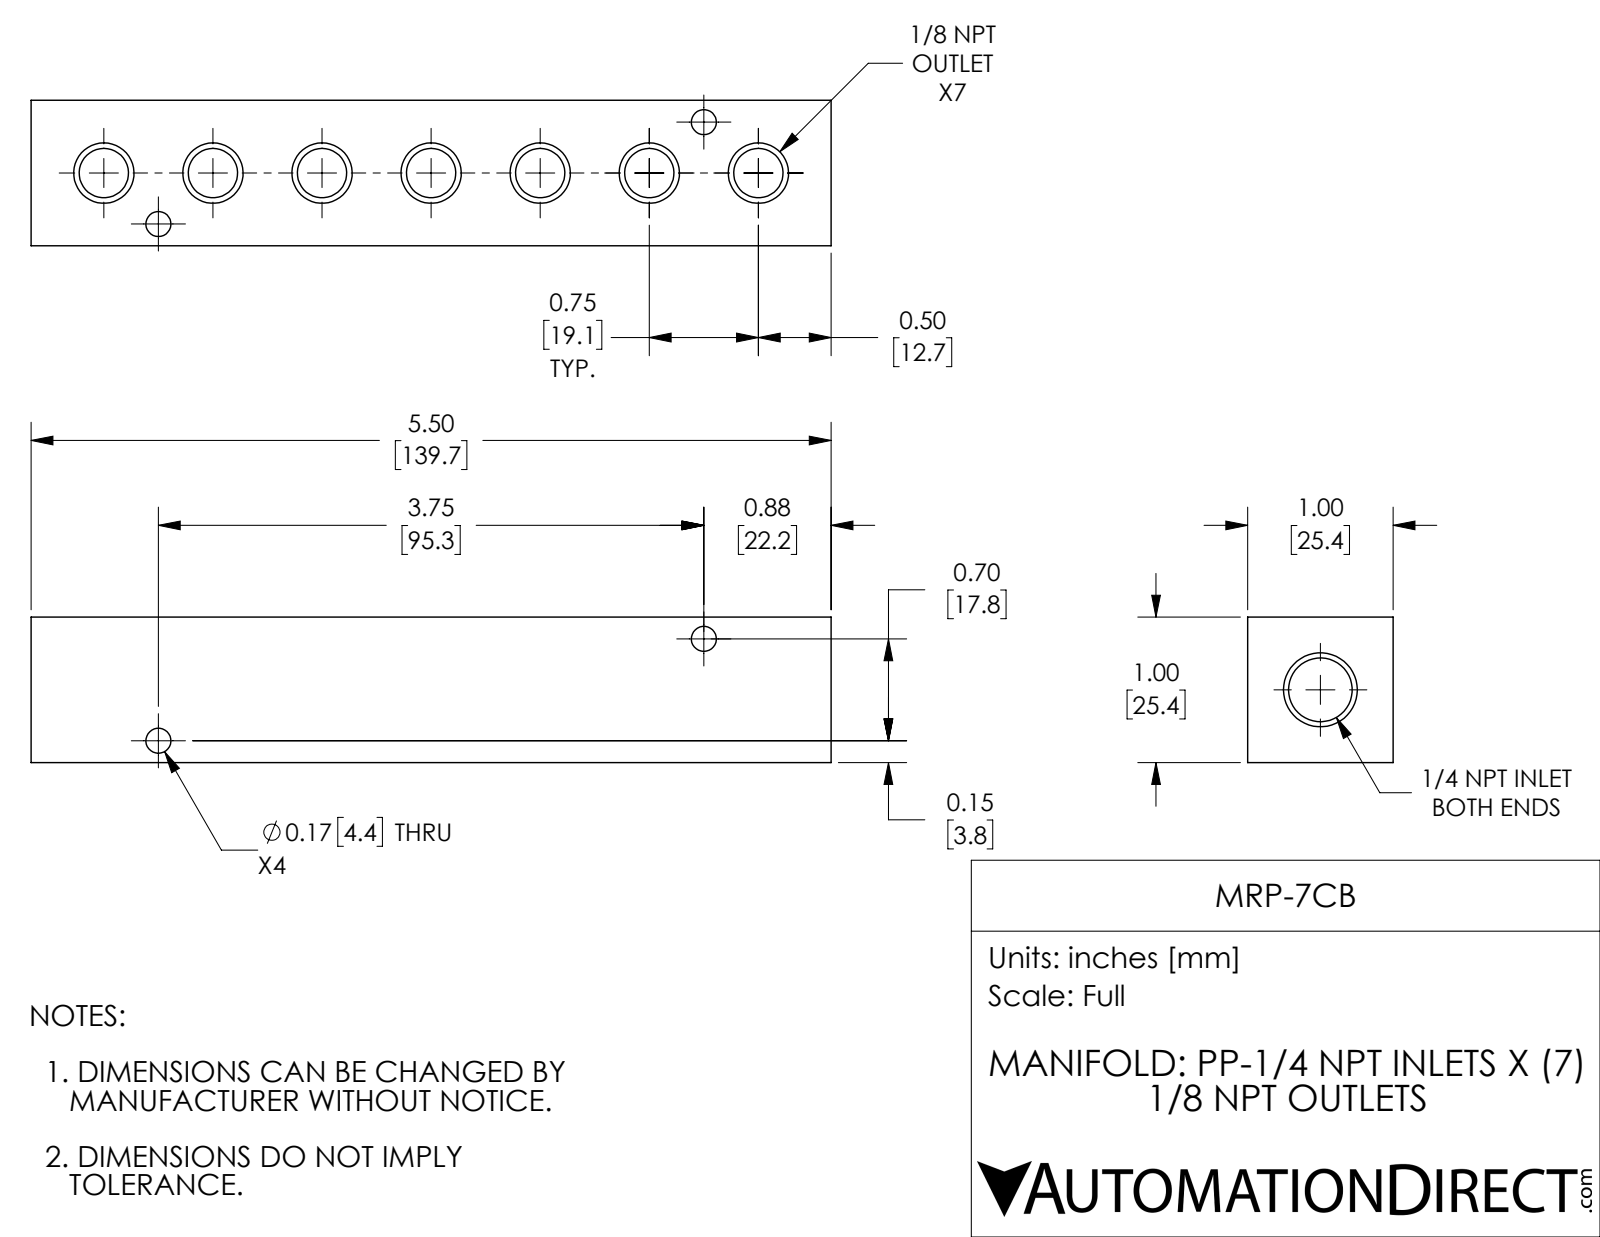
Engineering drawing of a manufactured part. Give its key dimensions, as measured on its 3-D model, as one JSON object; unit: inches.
{"part_name": "MRP-7CB", "step_written_by": "SolidWorks 2018 (AUTOMOTIVE_DESIGN)", "units": "inches", "bodies": {"solids": 1, "faces": 56, "planar": 6, "cylindrical": 32, "other": 18}, "overall_size": [5.5, 1, 1], "volume_in3": 4.389, "surface_area_in2": 33.85, "round_holes": [[0.339, 7], [0.172, 4], [0.438, 1]], "face_to_face_distances": [1, 5.5], "hole_center_spacings": [0.75, 1.5, 0.513, 2.25, 3, 1.178, 1.907, 2.648]}
